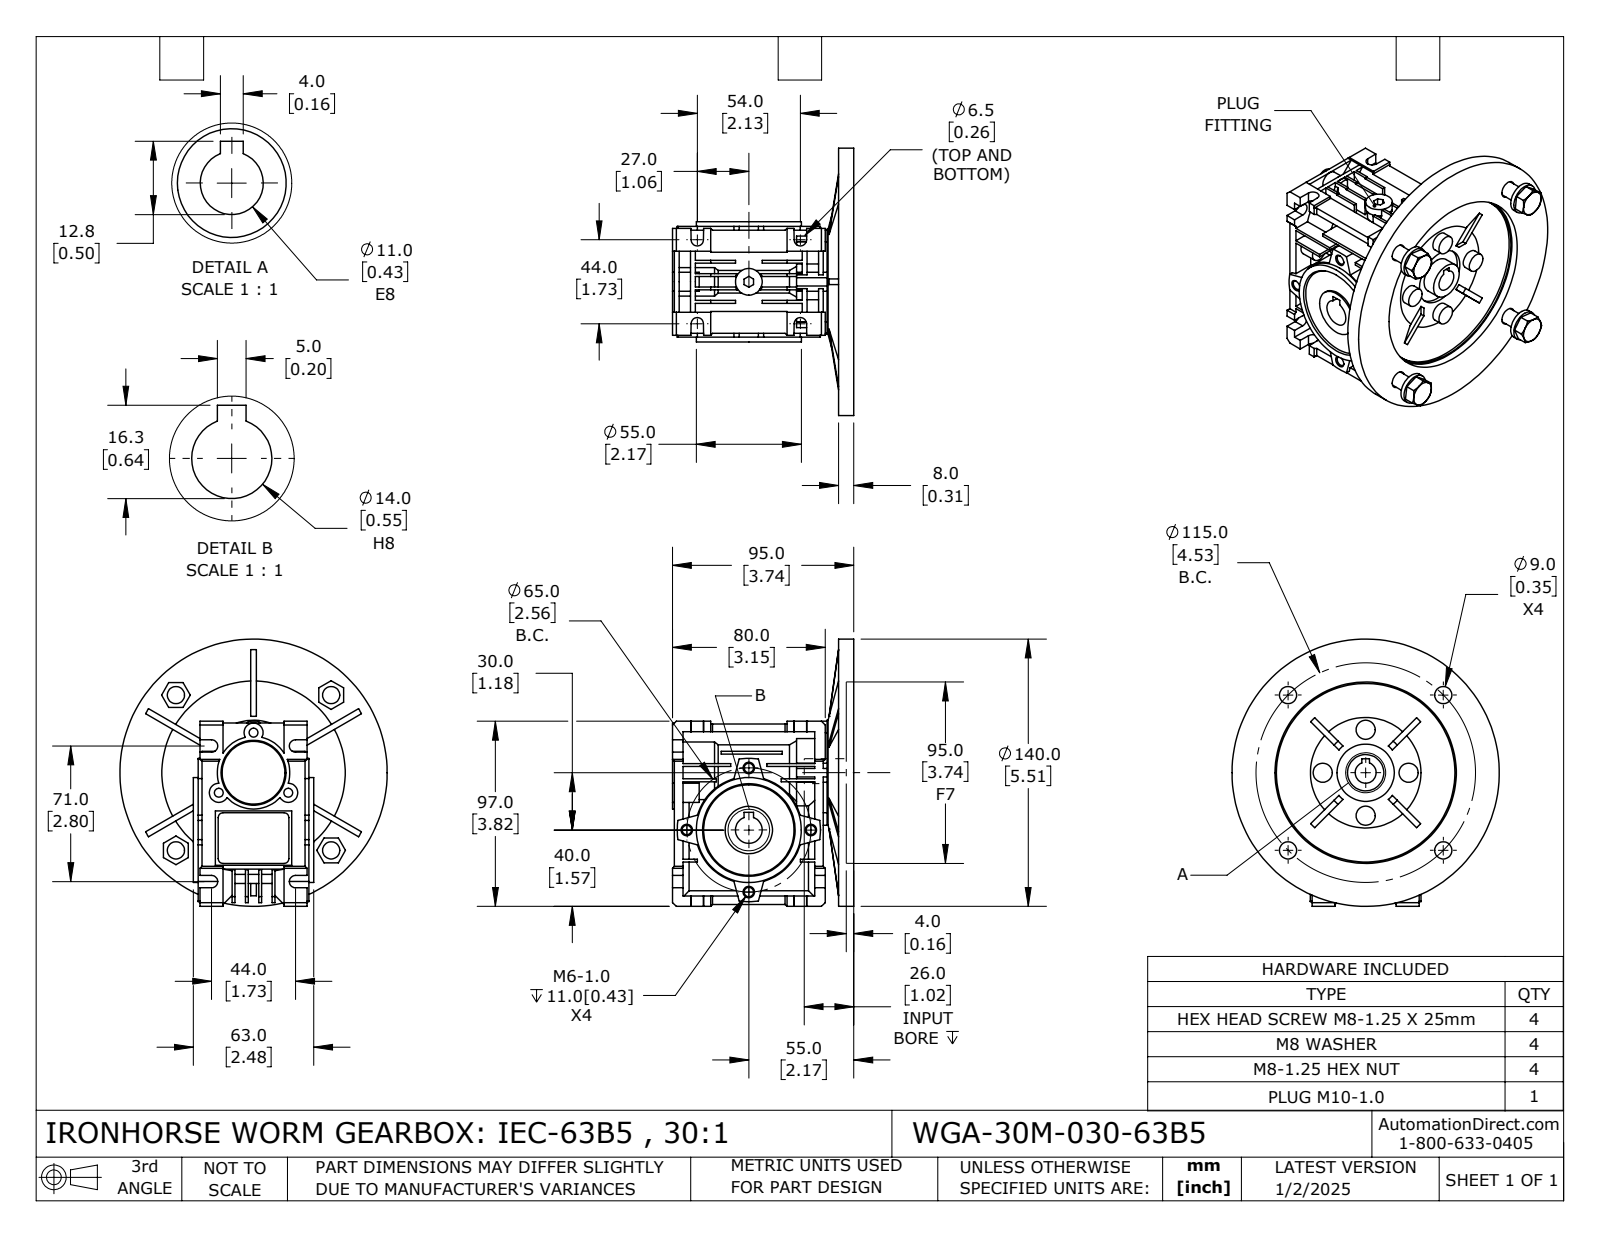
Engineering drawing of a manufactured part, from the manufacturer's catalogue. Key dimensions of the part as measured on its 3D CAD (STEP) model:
Part name (STEP PRODUCT): WGA-30M-030-63B5
STEP written by: SolidWorks 2024 (CONFIG_CONTROL_DESIGN)
Units: millimetres
Bodies: 18 solids, 1048 faces (618 planar, 256 cylindrical, 174 other)
Overall size (bounding box): 140 × 140 × 112.98
Volume: 404 435 mm³ · Surface area: 140 309 mm²
Round holes (diameter × count): ⌀9 ×5, ⌀4.92 ×4, ⌀6.8 ×4, ⌀8 ×4, ⌀9.12 ×4, ⌀4.65 ×3, ⌀4.92 ×2, ⌀11 ×1, ⌀11.5 ×1, ⌀14 ×1, ⌀14.5 ×1, ⌀19 ×1
Round bosses / shafts (diameter × count): ⌀16 ×4, ⌀10 ×4, ⌀55 ×2, ⌀140 ×1, ⌀56 ×1, ⌀38 ×1, ⌀37 ×1, ⌀14 ×1
Partial cylindrical surfaces — rounded edges, fillets, slot ends (radius × count): R3.25 ×8, R2.5 ×4, R5 ×3, R7.5 ×1, R17 ×1, R21.5 ×1, R37.5 ×1
Main face-to-face distances: 1.5, 8, 7, 5.5, 1, 14, 4, 4.5, 8.5, 2
Hole centre spacings: 32.5, 45.96, 57.5, 81.32, 21, 36.37, 37.61, 45.16
